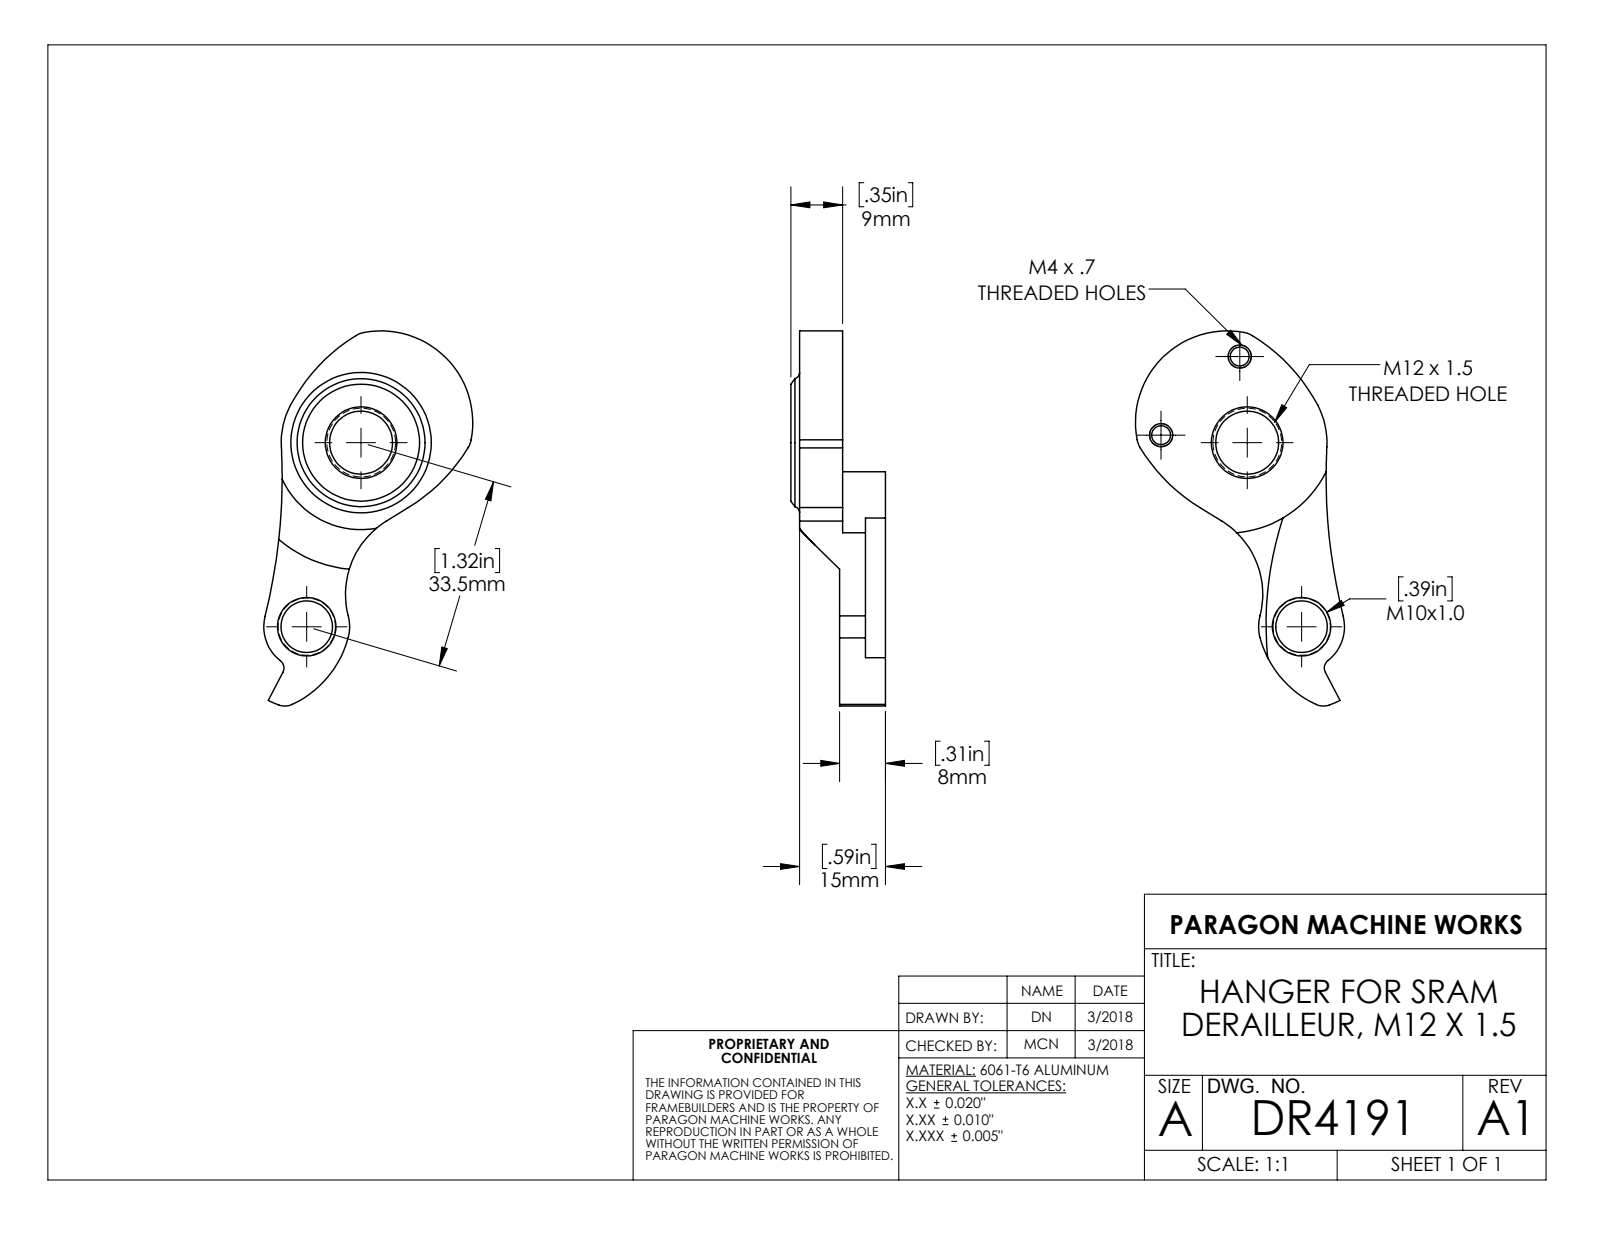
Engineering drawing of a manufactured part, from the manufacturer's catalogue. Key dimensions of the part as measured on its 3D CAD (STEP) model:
Part name (STEP PRODUCT): DR4191
STEP written by: SolidWorks 2018 (AUTOMOTIVE_DESIGN)
Units: millimetres
Bodies: 1 solid, 58 faces (8 planar, 29 cylindrical, 21 other)
Overall size (bounding box): 65.48 × 36.5 × 16.5
Volume: 9 143 mm³ · Surface area: 4 434 mm²
Round holes (diameter × count): ⌀3.3 ×2, ⌀9 ×1, ⌀11 ×1
Partial cylindrical surfaces — rounded edges, fillets, slot ends (radius × count): R4.27 ×2, R31.7 ×2, R1.65 ×1, R3 ×1, R7.5 ×1, R13.95 ×1, R14.5 ×1, R15 ×1
Main face-to-face distances: 7.5, 15, 8, 0.5, 7, 16.5, 9, 8.5, 1.5, 3.5
Hole centre spacings: 15.09, 19.42, 33.5, 41.46, 48.37
